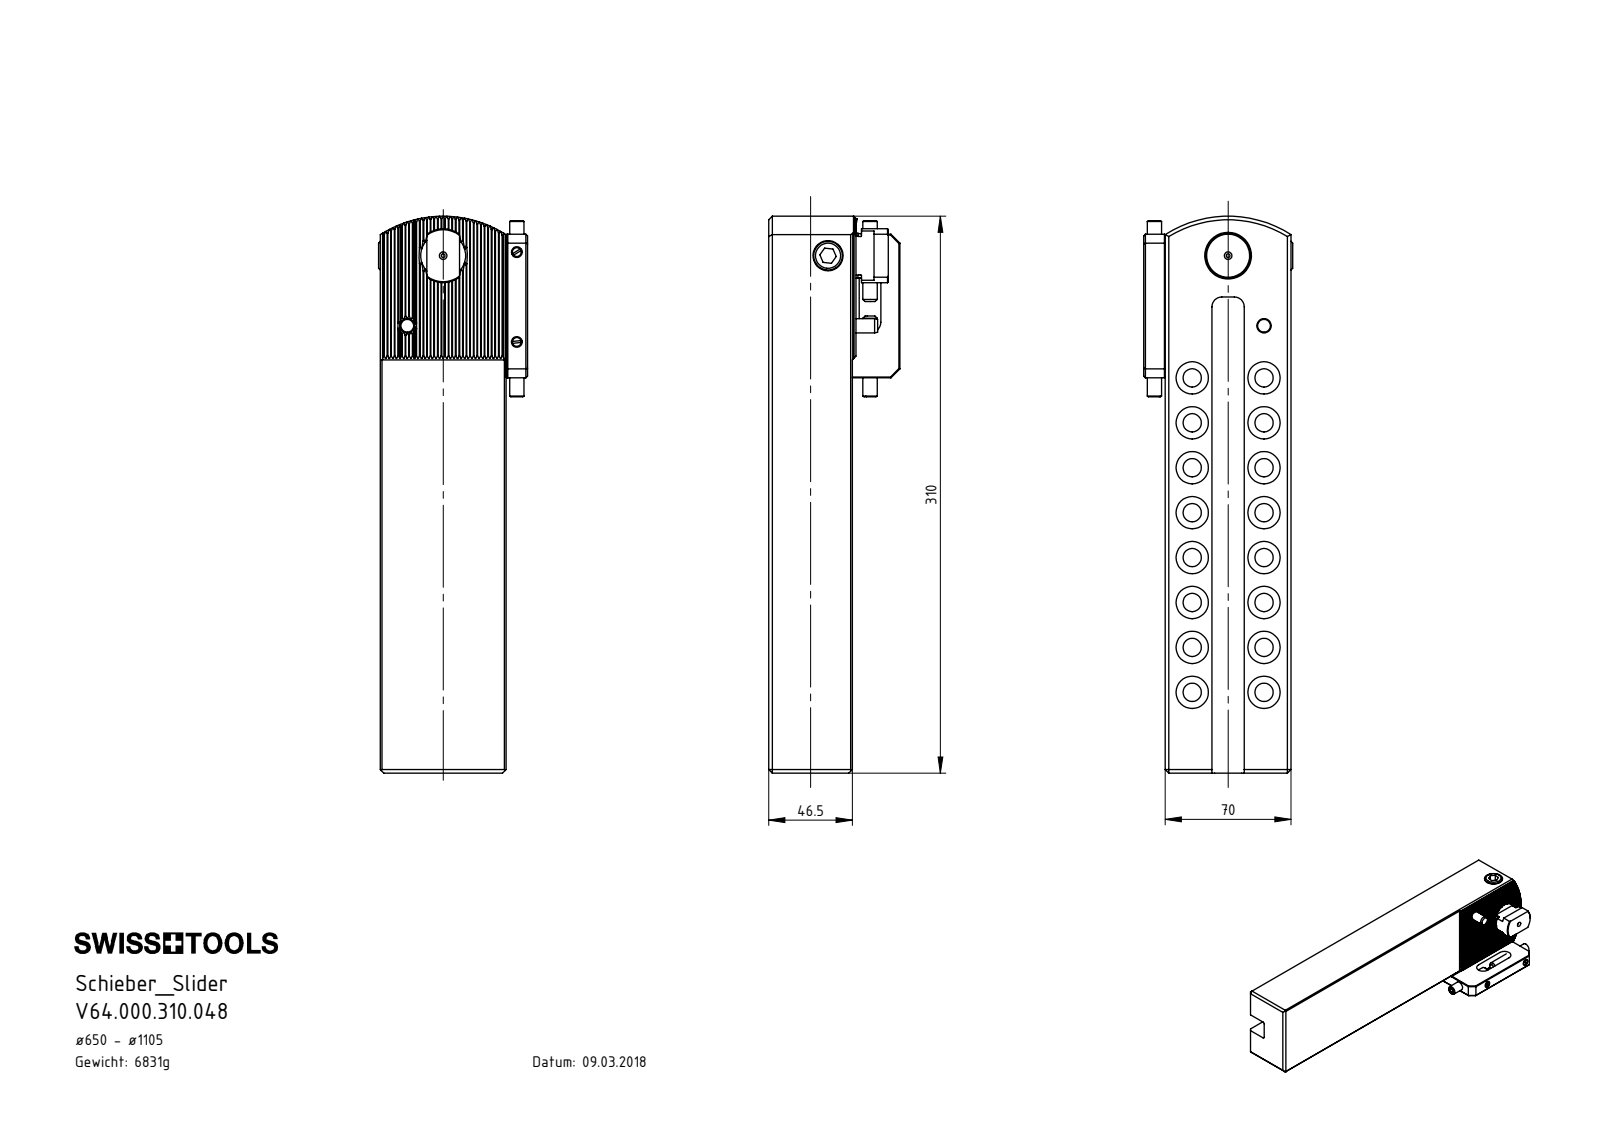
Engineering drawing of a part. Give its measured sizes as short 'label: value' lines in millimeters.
name: VK1-ER3.001.028_A; VK1-ER2.001.044_A; DIN 7984 - M10 x 16; VK3.VK1.310.048 (+8 more)
written by: SolidWorks 2017 (AUTOMOTIVE_DESIGN)
unit: mm
bodies: 14 solids, 519 faces (314 planar, 126 cylindrical, 79 other)
size: 310 × 83 × 73
volume: 873 101 mm³; area: 145 352 mm²
holes: 17× ⌀18, 16× ⌀10.2, 2× ⌀5, 2× ⌀6, 2× ⌀6.8, 1× ⌀2, 1× ⌀8, 1× ⌀8.5, 1× ⌀10.5, 1× ⌀11, 1× ⌀14, 1× ⌀25
bosses: 2× ⌀16, 2× ⌀6, 1× ⌀10, 1× ⌀8
rounds: 33× R0.14, 4× R2, 3× R1.5, 2× R5.5, 2× R6, 1× R12.3, 1× R15, 1× R65
face distances: 70, 46.5, 44, 26, 26.5, 18, 20, 12, 38, 56
hole spacings: 25, 47.17, 50, 64.03, 75, 85, 40, 100
